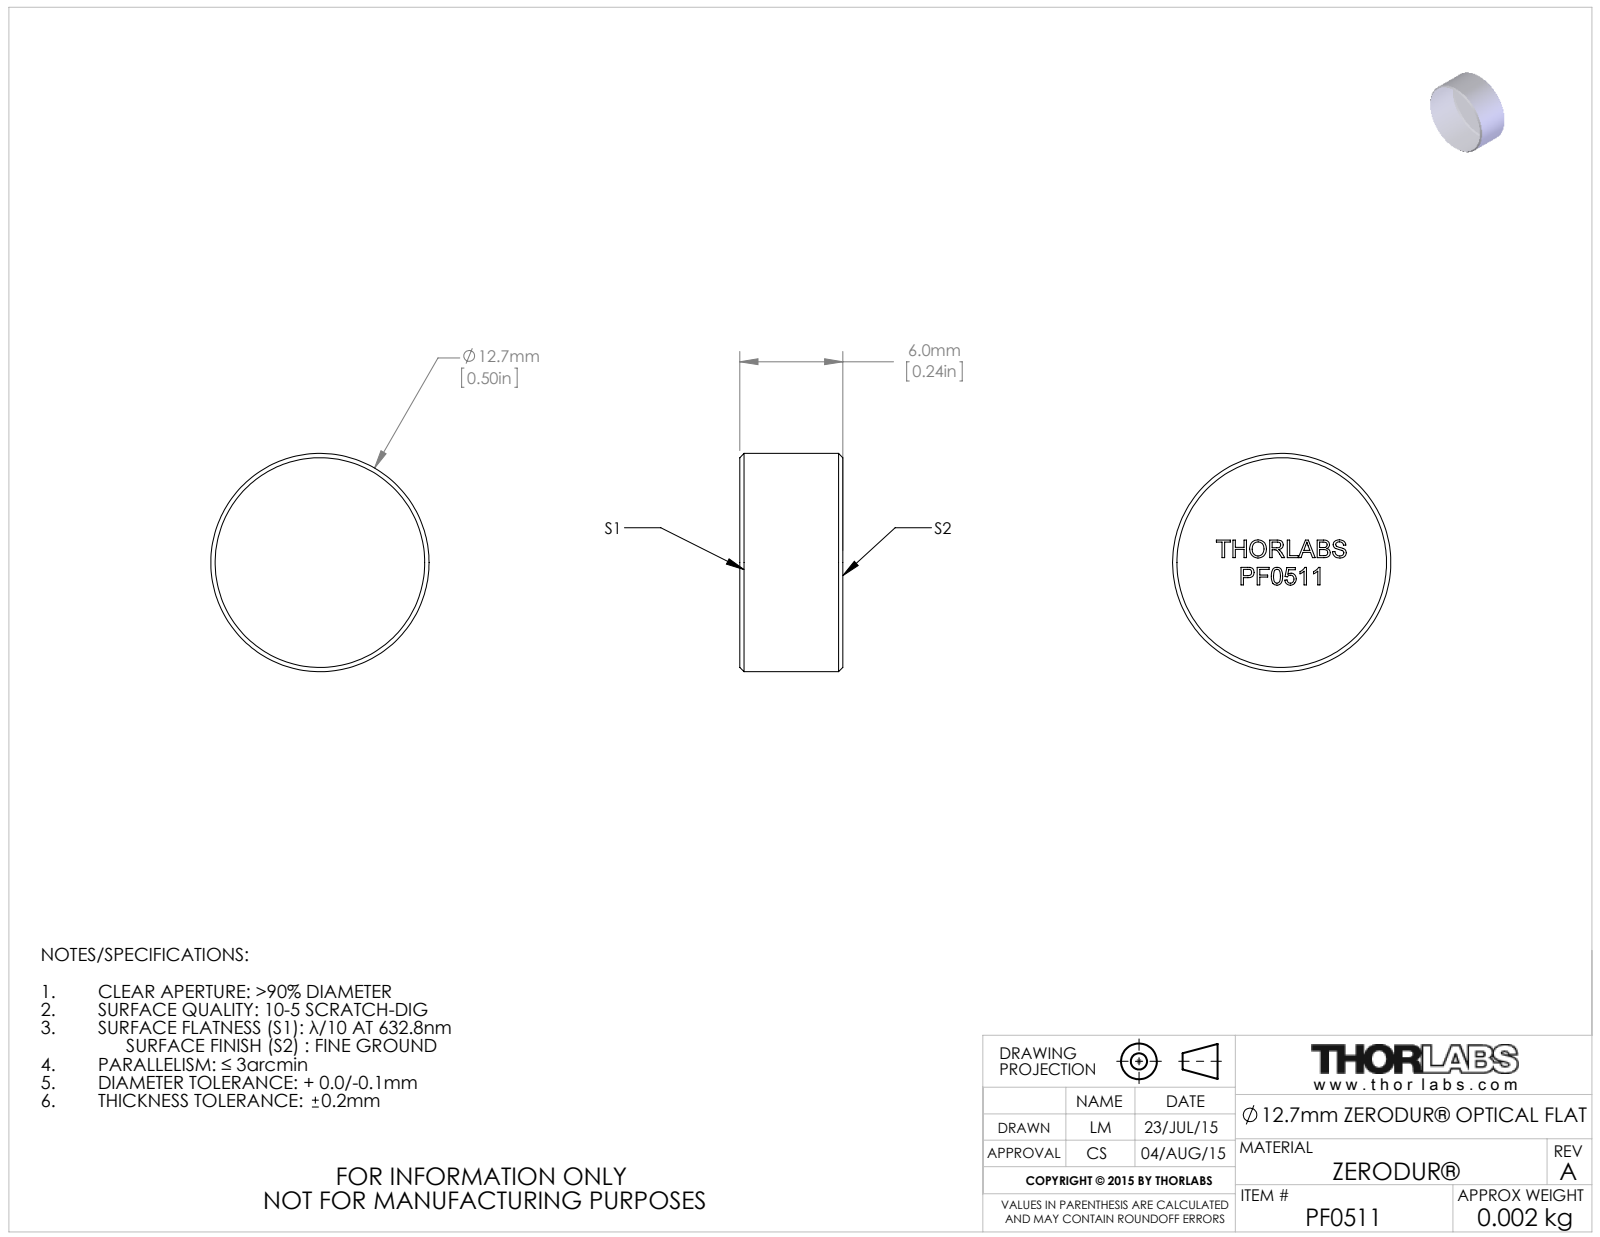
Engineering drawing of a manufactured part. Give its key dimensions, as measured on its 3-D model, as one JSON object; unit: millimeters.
{"part_name": "TTN045228-E0W", "step_written_by": "SolidWorks 2014 (CONFIG_CONTROL_DESIGN)", "units": "millimeters", "bodies": {"solids": 1, "faces": 194, "planar": 117, "cylindrical": 2, "other": 75}, "overall_size": [12.7, 12.7, 6], "volume_mm3": 758, "surface_area_mm2": 481, "round_bosses_or_shafts": [[12.7, 1]], "face_to_face_distances": [6, 0.79, 0.91, 1.03, 1.74, 4.28, 1.58, 1.28, 0.32, 3.49]}
